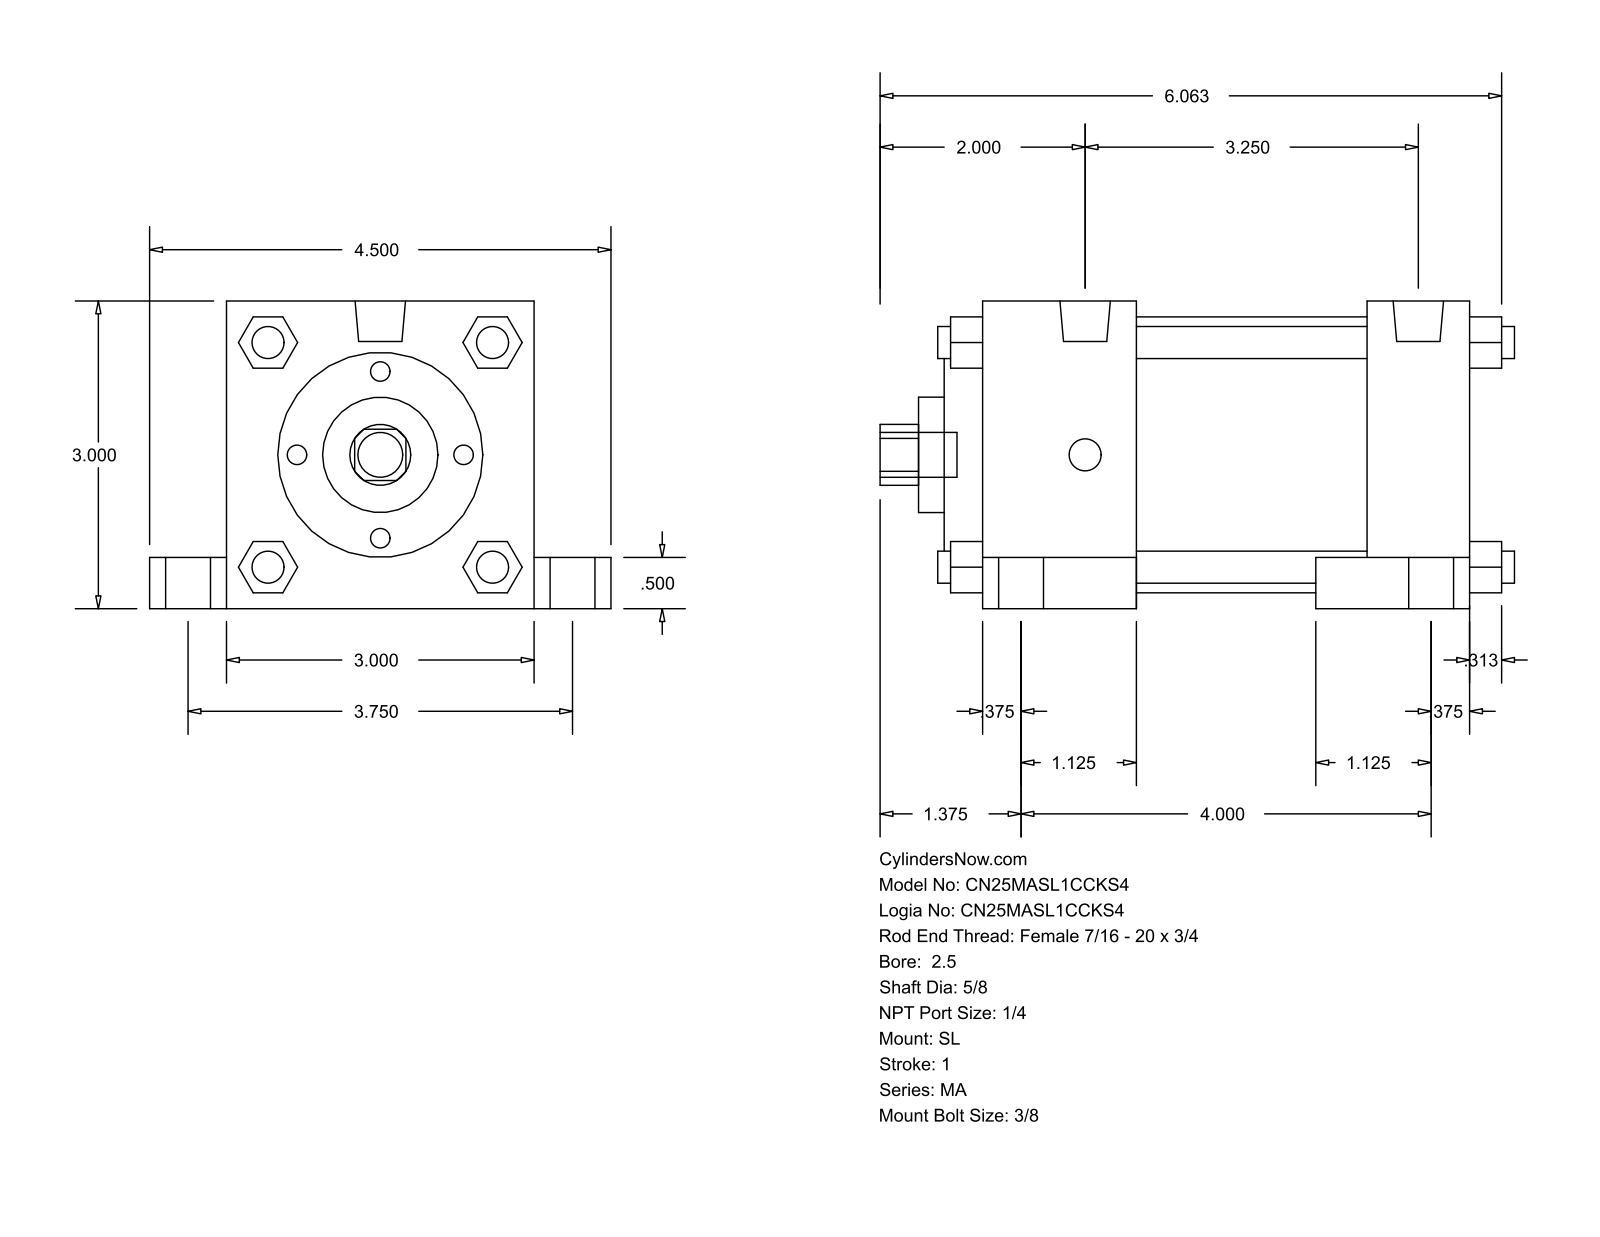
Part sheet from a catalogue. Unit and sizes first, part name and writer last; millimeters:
Units: millimetres
Overall size (bounding box): 157.16 × 114.3 × 76.2
Round holes (diameter × count): ⌀15.88 ×1, ⌀28.57 ×1, ⌀50.8 ×1, ⌀68.33 ×1
Round bosses / shafts (diameter × count): ⌀7.94 ×8, ⌀11.11 ×5, ⌀17.46 ×4, ⌀12.49 ×2
Partial cylindrical surfaces — rounded edges, fillets, slot ends (radius × count): R7.54 ×1
Main face-to-face distances: 76.2, 95.25, 120.65, 12.7, 57.15, 25.4, 38.1, 82.55, 19.05, 63.5
Bodies: 0 solids, 150 faces (113 planar, 37 cylindrical, 0 other)
Part name (STEP PRODUCT): MA_SL__0250_0.625
STEP written by: GSSL Pune (CONFIG_CONTROL_DESIGN)
